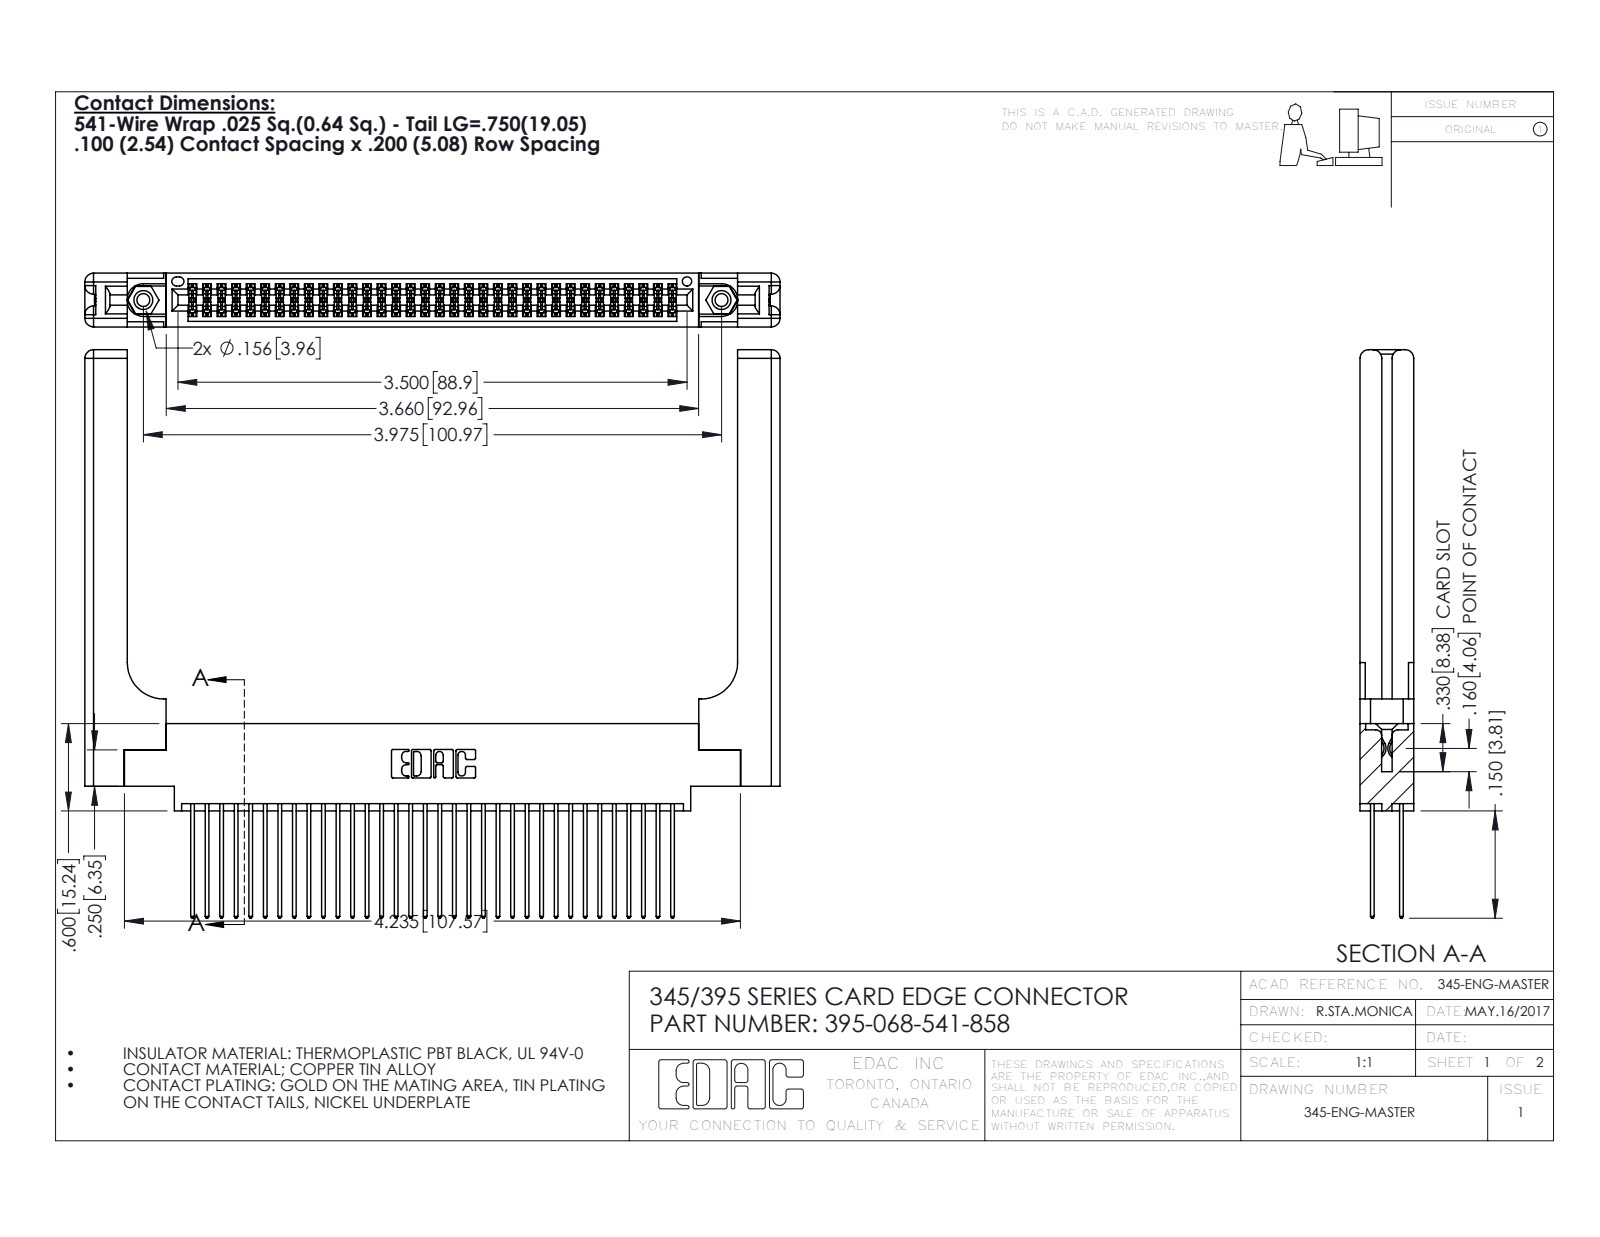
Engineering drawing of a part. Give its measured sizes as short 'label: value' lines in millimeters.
name: 345-220-058_345-220-058; 345-250-001_345-250-001-102; 345 Part_0.170 Offset - 0.156 Dia-TH; 345-292-001_345-293-141 (+1 more)
written by: SolidWorks 2016 (CONFIG_CONTROL_DESIGN)
unit: mm
bodies: 73 solids, 3786 faces (2476 planar, 1250 cylindrical, 60 other)
size: 121.4 × 99.2 × 9.4
volume: 20 470 mm³; area: 24 610 mm²
holes: 2× ⌀2.3, 2× ⌀3.2, 2× ⌀4, 1× ⌀1.6
bosses: 2× ⌀3.9
rounds: 102× R0.2, 68× R0.3, 22× R0.3, 16× R1.5, 6× R0.2, 6× R0.8, 3× R0.7, 2× R0.4
face distances: 1.8, 7.6, 9.4, 2.5, 6.9, 0.6, 5.1, 5.7, 4.4, 3.8
hole spacings: 6.9, 95, 101
